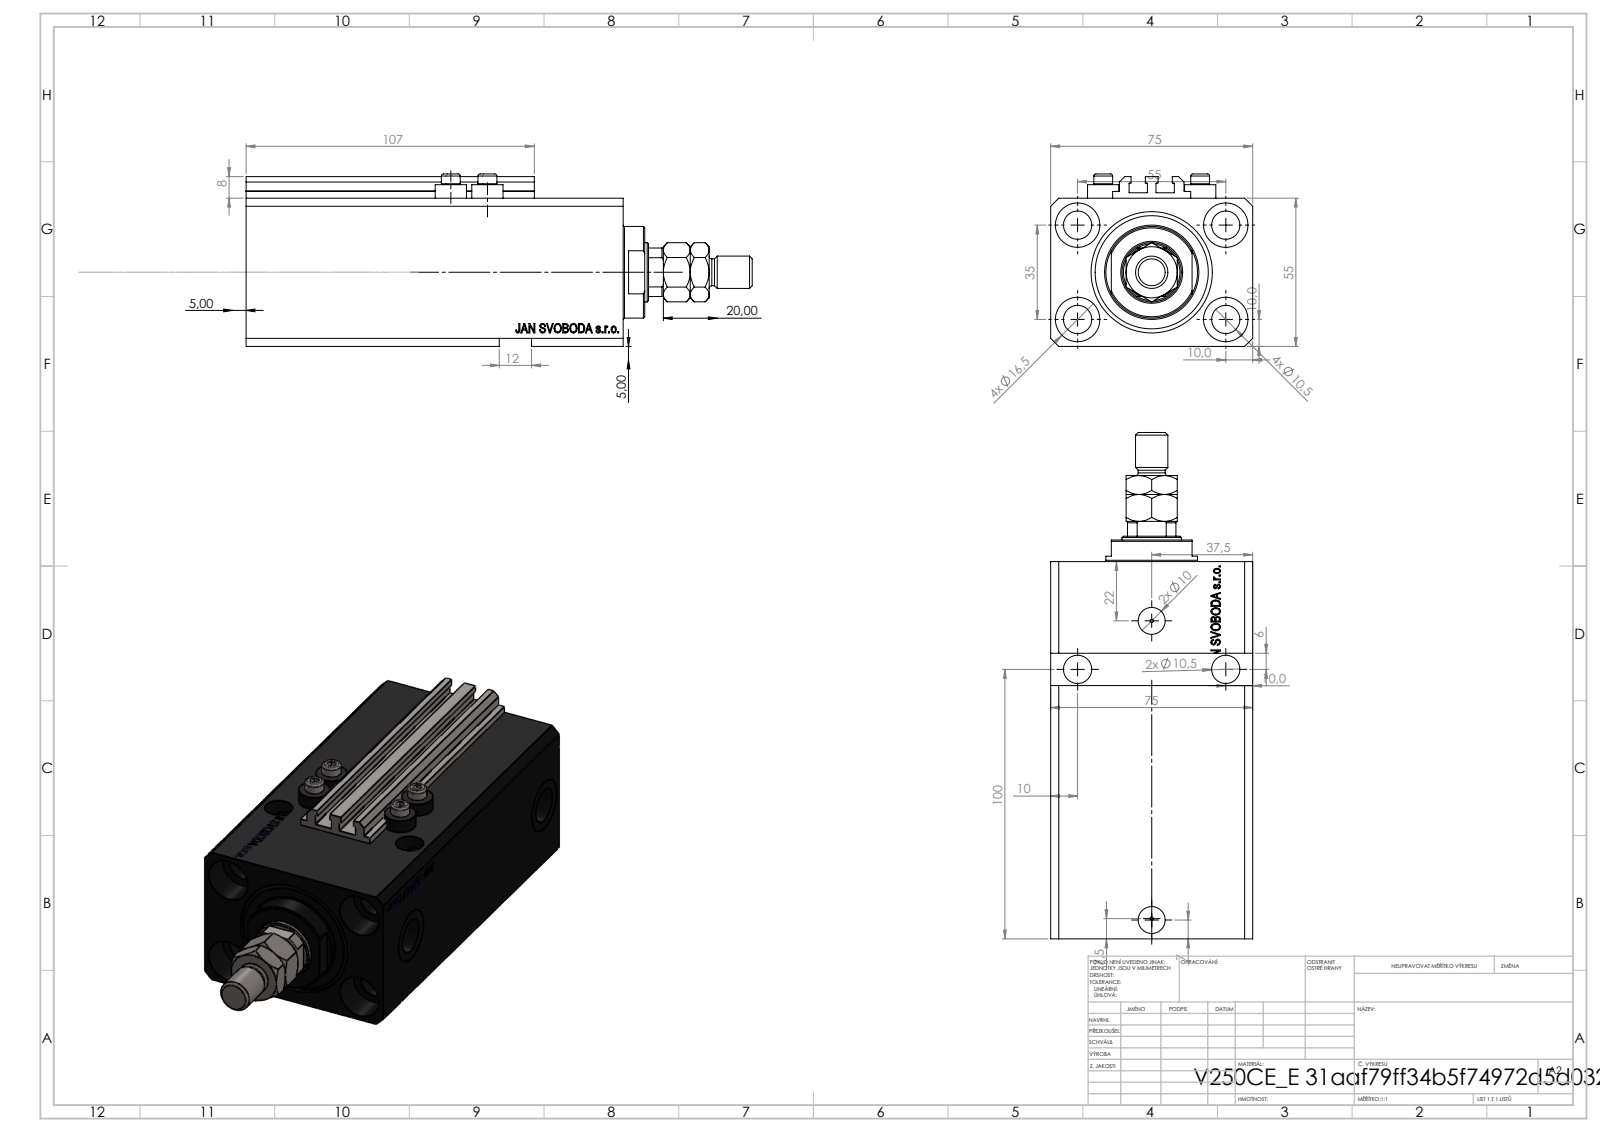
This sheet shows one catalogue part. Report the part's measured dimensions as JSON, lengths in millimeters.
{"part_name": "V250CE_E_Body; MTA; ALLEN BOLT V250CE; V250CE_C_VCP (+1 more)", "step_written_by": "SolidWorks 2019 (CONFIG_CONTROL_DESIGN)", "units": "millimeters", "bodies": {"solids": 9, "faces": 1133, "planar": 529, "cylindrical": 150, "other": 454}, "overall_size": [188, 75, 64], "volume_mm3": 492194, "surface_area_mm2": 117621, "round_holes": [[10.5, 9], [1.25, 4], [4, 4], [16.5, 4], [10, 2], [13.16, 2], [20, 2], [22, 1], [32, 1], [45, 1]], "round_bosses_or_shafts": [[11.6, 4], [7, 4], [34, 1], [12, 1], [10, 1]], "partial_cylinders_radius": [[0.2, 10], [10.5, 1]], "face_to_face_distances": [55, 75, 15, 140, 125, 2.5, 9.9, 3, 57, 115.1], "hole_center_spacings": [32.6, 32.87, 55, 96.98, 13.6, 14.09, 25.81, 32.58]}
